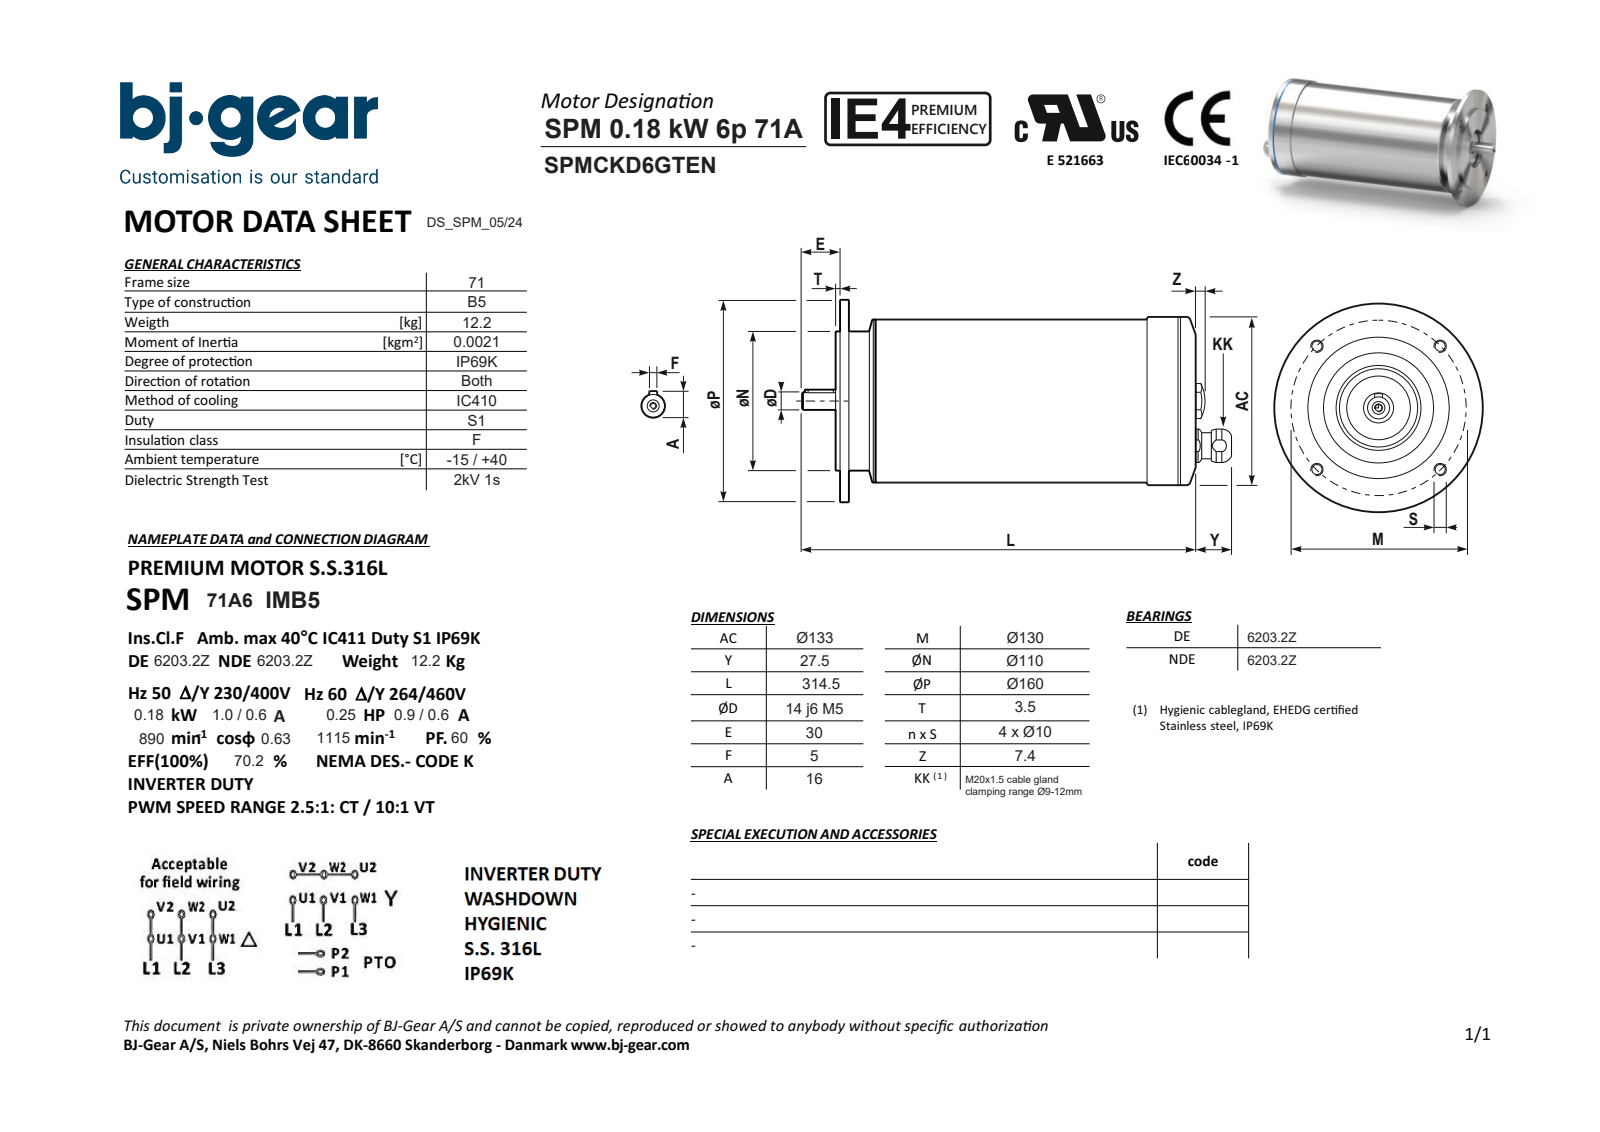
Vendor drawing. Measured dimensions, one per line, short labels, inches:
name: SPMCKD6GTENN4KSA1-N---NNN
written by: Solid Edge (AUTOMOTIVE_DESIGN)
unit: in
bodies: 1 solid, 86 faces (31 planar, 30 cylindrical, 25 other)
size: 13.425 × 6.299 × 6.299
volume: 228.4 in³; area: 259.2 in²
holes: 4× ⌀0.394, 1× ⌀0.163, 1× ⌀0.209, 1× ⌀0.276, 1× ⌀0.528, 1× ⌀2.047
bosses: 1× ⌀6.299, 1× ⌀5.236, 1× ⌀5.235, 1× ⌀5.079, 1× ⌀5.078, 1× ⌀4.331, 1× ⌀0.787, 1× ⌀0.669
rounds: 2× R0.098, 1× R0.504
face distances: 0.276, 10.886, 11.161, 11.299, 0.413, 0.138, 10.945, 0.059, 0.217, 0.354
hole spacings: 2.559, 3.619, 1.87, 3.631, 5.118, 1.339
